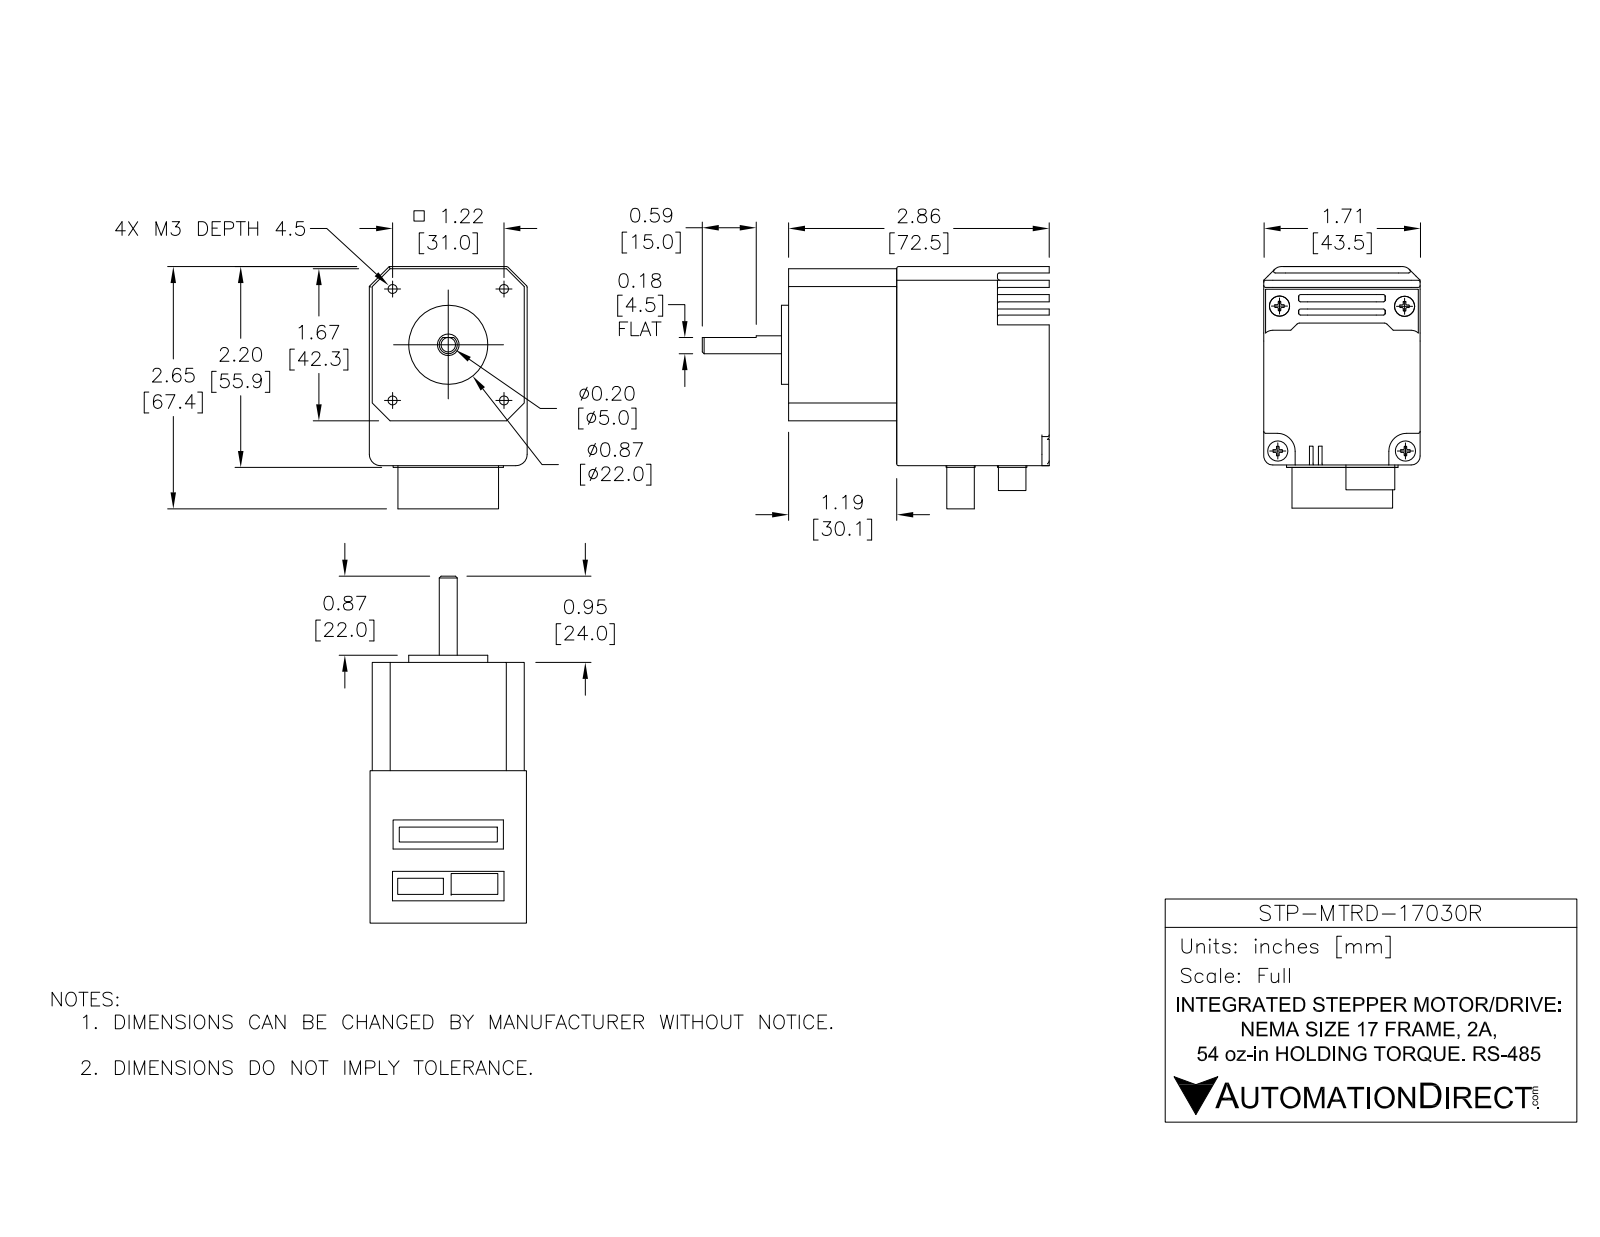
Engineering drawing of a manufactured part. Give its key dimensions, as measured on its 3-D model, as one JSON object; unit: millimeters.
{"part_name": "STP-MTRD-17030R", "step_written_by": "SolidWorks 2017 (AUTOMOTIVE_DESIGN)", "units": "millimeters", "bodies": {"solids": 2, "faces": 397, "planar": 149, "cylindrical": 157, "other": 91}, "overall_size": [96.5, 55.85, 43.5], "volume_mm3": 142404, "surface_area_mm2": 23094, "round_holes": [[3, 4], [7.5, 1], [15, 1]], "round_bosses_or_shafts": [[5.6, 4], [22, 1], [5, 1]], "partial_cylinders_radius": [[0.5, 75], [2.5, 12], [0.68, 4], [10.96, 4], [25.37, 4], [5, 2], [0.75, 1]], "face_to_face_distances": [2, 1.8, 41.7, 43.5, 39.9, 72.5, 4, 41.1, 1.2, 55.2], "hole_center_spacings": [21.92, 31, 43.84]}
